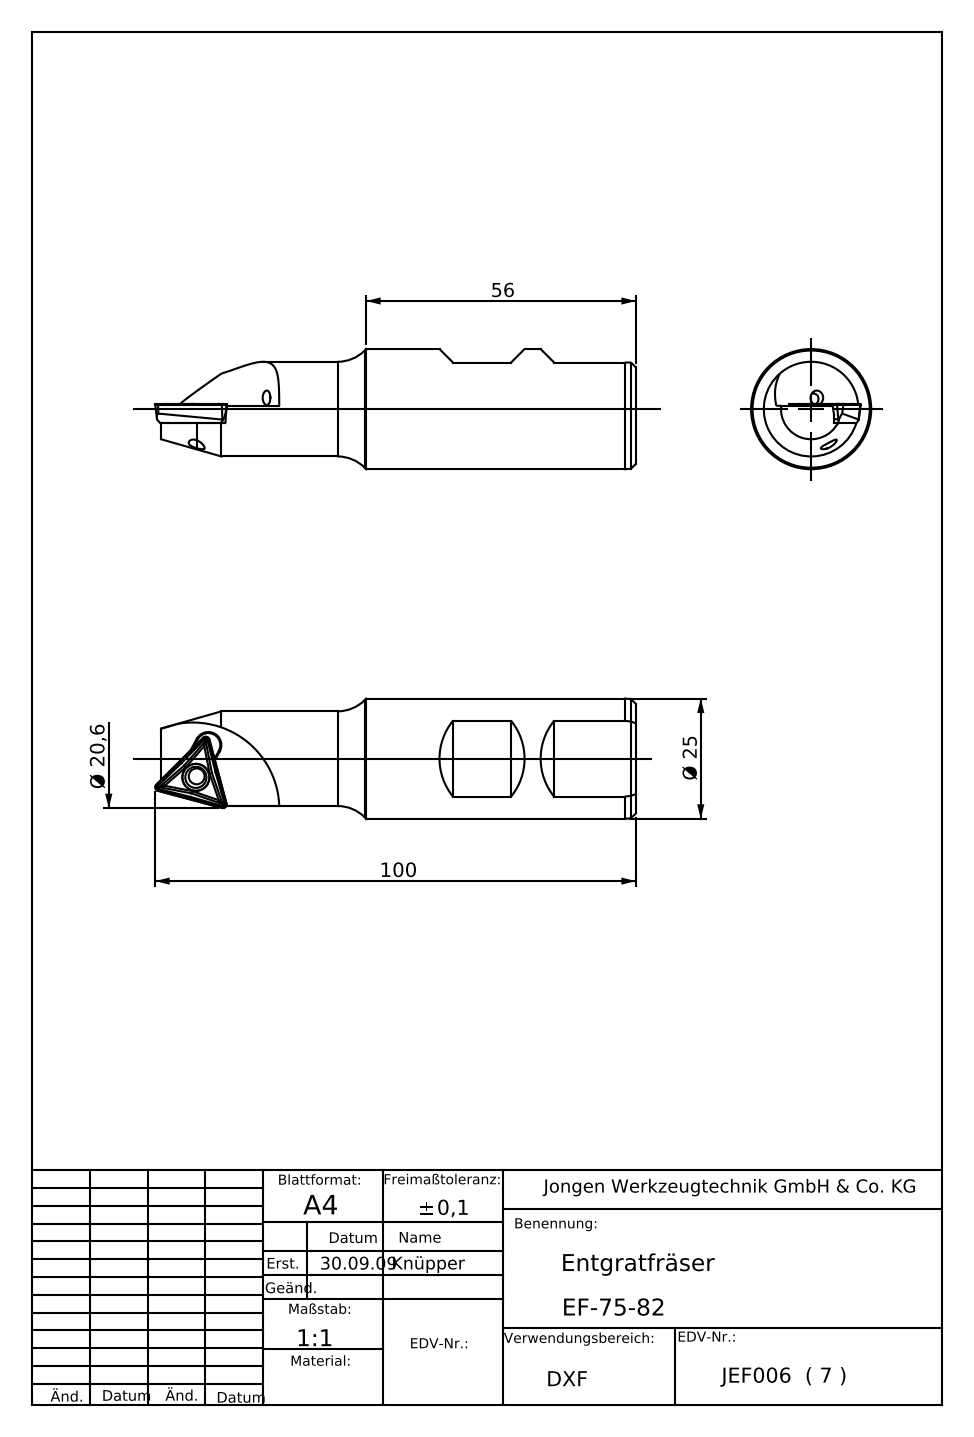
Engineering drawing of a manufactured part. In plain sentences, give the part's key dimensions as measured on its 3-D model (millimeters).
The part is named "EF-75-82". Its 3-D file was written by "SolidWorks 2014 (AUTOMOTIVE_DESIGN)". It is 1 solid with 39 faces: 23 planar, 5 cylindrical and 11 other. Overall it measures 100 by 25 by 25 millimeters. Its volume is 35 314 cubic millimeters and its surface area 9 661 square millimeters. Round holes: 1 of diameter 3, 1 of diameter 6.5. Round bosses or shafts: 1 of diameter 25, 1 of diameter 19.7. Partial cylindrical surfaces (rounded edges, fillets, slot ends): 1 of radius 18. The main face-to-face distances are 9.01, 14.88, 98.8, 11.31, 26.19, 3.67, 12.68, 5.01.
